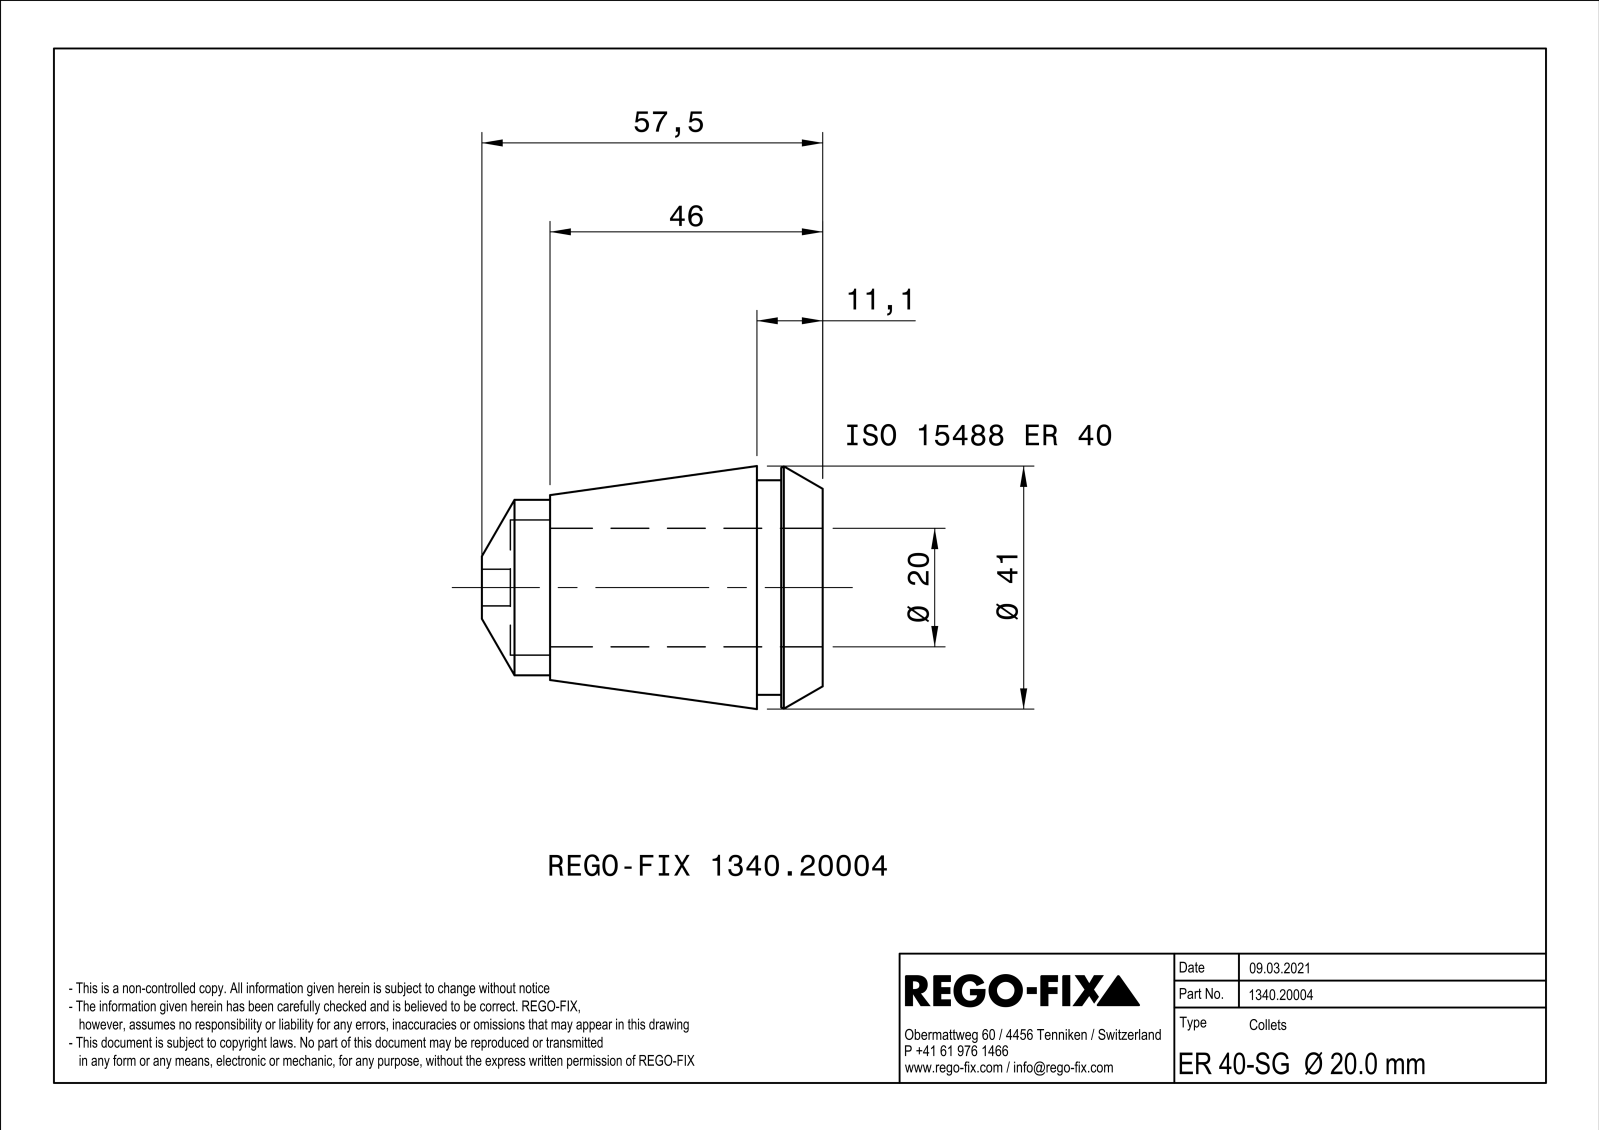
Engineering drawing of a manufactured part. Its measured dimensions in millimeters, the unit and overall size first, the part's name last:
Units: millimetres
Overall size (bounding box): 61.8 × 40.85 × 40.85
Round holes (diameter × count): ⌀3 ×1, ⌀20 ×1, ⌀22.8 ×1, ⌀25 ×1, ⌀26 ×1, ⌀28.2 ×1
Round bosses / shafts (diameter × count): ⌀36.2 ×1, ⌀29.6 ×1, ⌀25.8 ×1, ⌀25.5 ×1, ⌀24.8 ×1, ⌀7 ×1, ⌀4.4 ×1
Partial cylindrical surfaces — rounded edges, fillets, slot ends (radius × count): R3.09 ×1
Main face-to-face distances: 1, 52.7, 7, 45.7, 4.1, 11.1, 41.6, 6.7, 46, 39
Volume: 32 033 mm³ · Surface area: 20 536 mm²
Bodies: 1 solid, 283 faces (151 planar, 36 cylindrical, 96 other)
Part name (STEP PRODUCT): NOCUT
STEP written by: SIEMENS PLM Software Solid Edge ST10 (AUTOMOTIVE_DESIGN)
